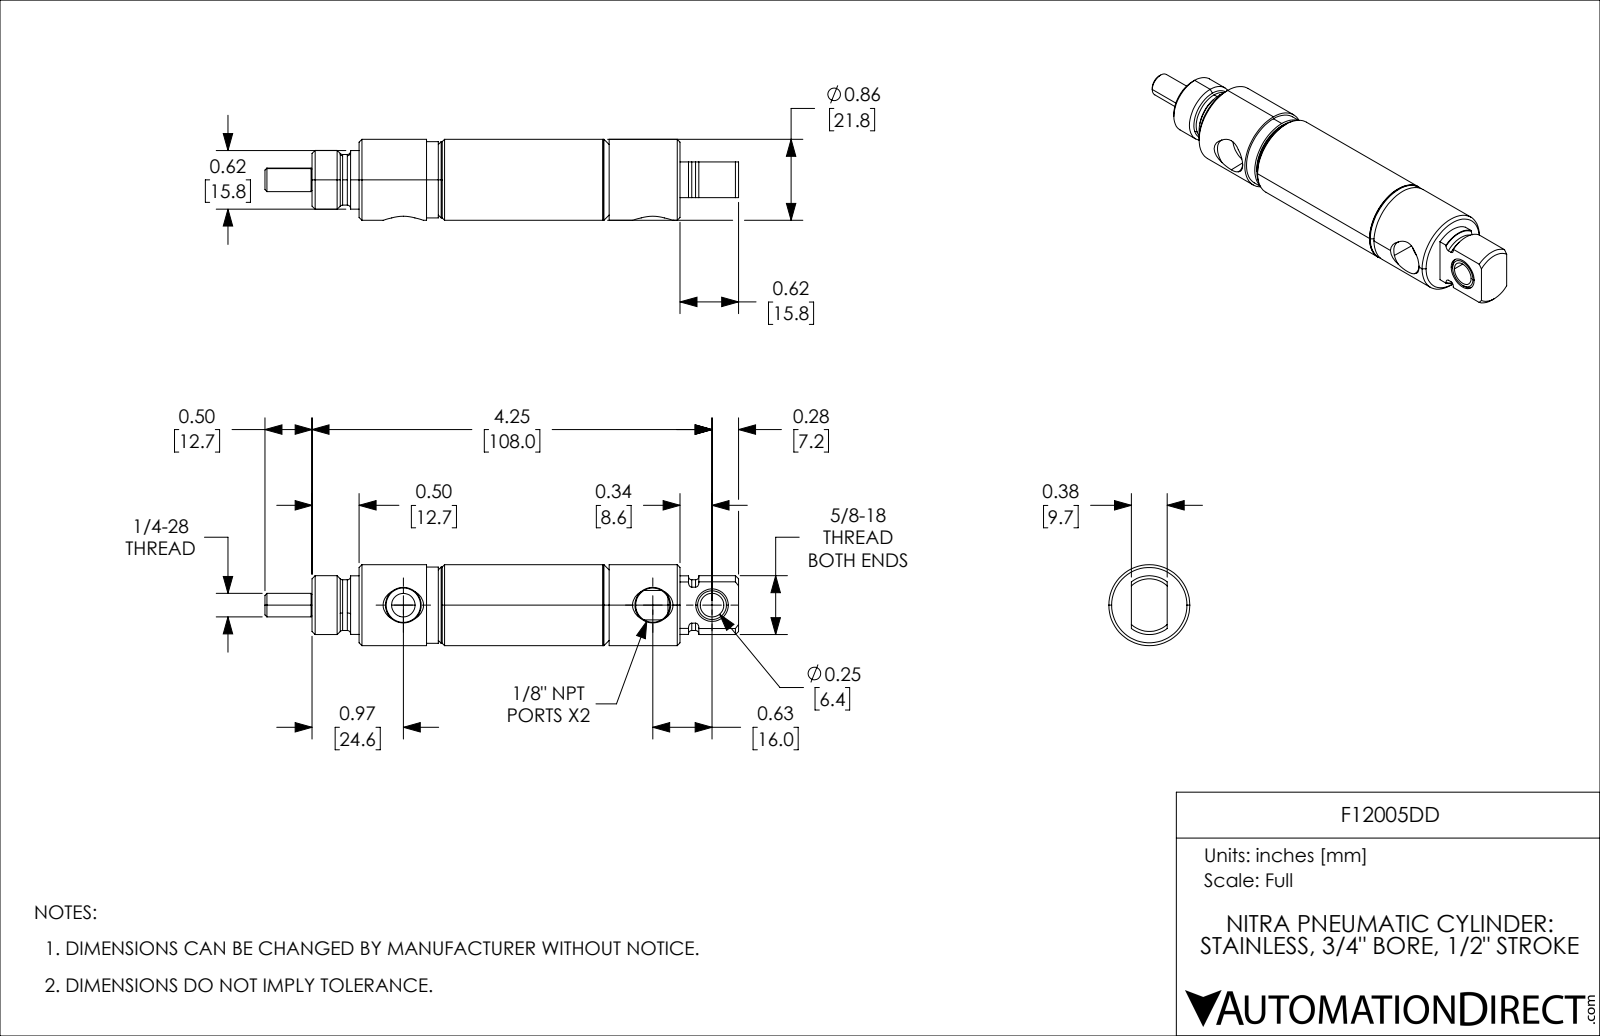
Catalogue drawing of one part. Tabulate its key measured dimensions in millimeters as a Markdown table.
| quantity | value |
| --- | --- |
| part name | F12005DD_5; F12005DD_3; F12005DD_7; F12005DD_11 (+2 more) |
| STEP written by | SolidWorks 2021 (CONFIG_CONTROL_DESIGN) |
| units | millimeters |
| bodies | 5 solids, 158 faces (29 planar, 61 cylindrical, 68 other) |
| overall size | 127.81 × 21.84 × 21.84 |
| volume | 30 711 mm³ |
| surface area | 18 333 mm² |
| round holes (diameter × count) | 6.35 × 1, 6.38 × 1, 6.95 × 1, 7.92 × 1, 8.78 × 1, 9.23 × 1, 12.7 × 1, 17.83 × 1 |
| round bosses / shafts (diameter × count) | 21.84 × 1, 20.57 × 1, 19.35 × 1, 15.88 × 1, 15.81 × 1, 13.68 × 1, 6.35 × 1, 5.84 × 1 |
| partial cylindrical surfaces (radius × count) | 6.84 × 1 |
| main face-to-face distances | 40.49, 12.7, 21.43, 61.92, 46.12, 74.62, 34.13, 58.82, 24.69, 19.12 |
| hole center spacings | 16, 67.31, 83.31 |
